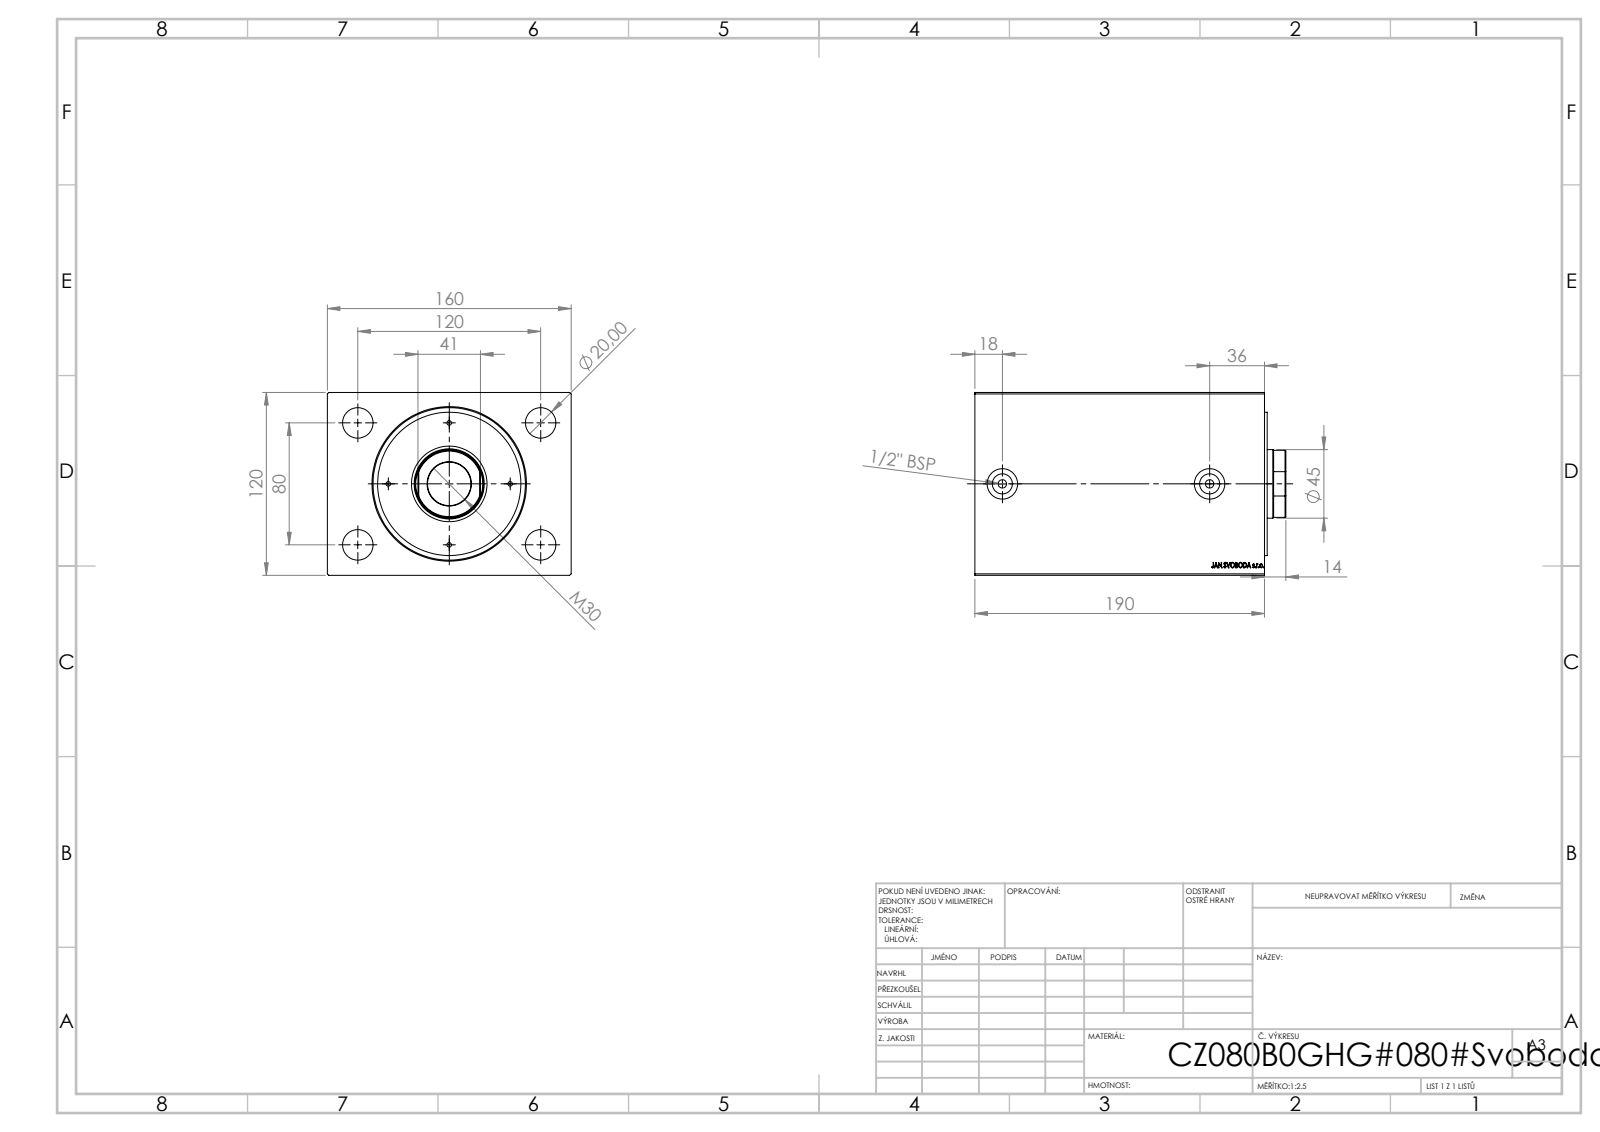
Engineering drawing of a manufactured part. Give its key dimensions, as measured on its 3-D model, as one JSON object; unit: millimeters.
{"part_name": "V500CZ_B_VC; V500CZ", "step_written_by": "SolidWorks 2019 (CONFIG_CONTROL_DESIGN)", "units": "millimeters", "bodies": {"solids": 3, "faces": 874, "planar": 400, "cylindrical": 58, "other": 416}, "overall_size": [204, 160, 120], "volume_mm3": 3287000, "surface_area_mm2": 266922, "round_holes": [[20, 6], [3, 4], [5.5, 2], [13.16, 2], [28.5, 1], [36, 1], [45, 1], [46, 1], [80, 1], [100, 1]], "round_bosses_or_shafts": [[94, 1]], "partial_cylinders_radius": [[22, 1]], "face_to_face_distances": [120, 160, 190, 164.7, 25.3, 14, 1.8, 12.2, 152.5, 177.8], "hole_center_spacings": [40, 44.72, 56.57, 60, 72.11, 80, 100, 107.7]}
